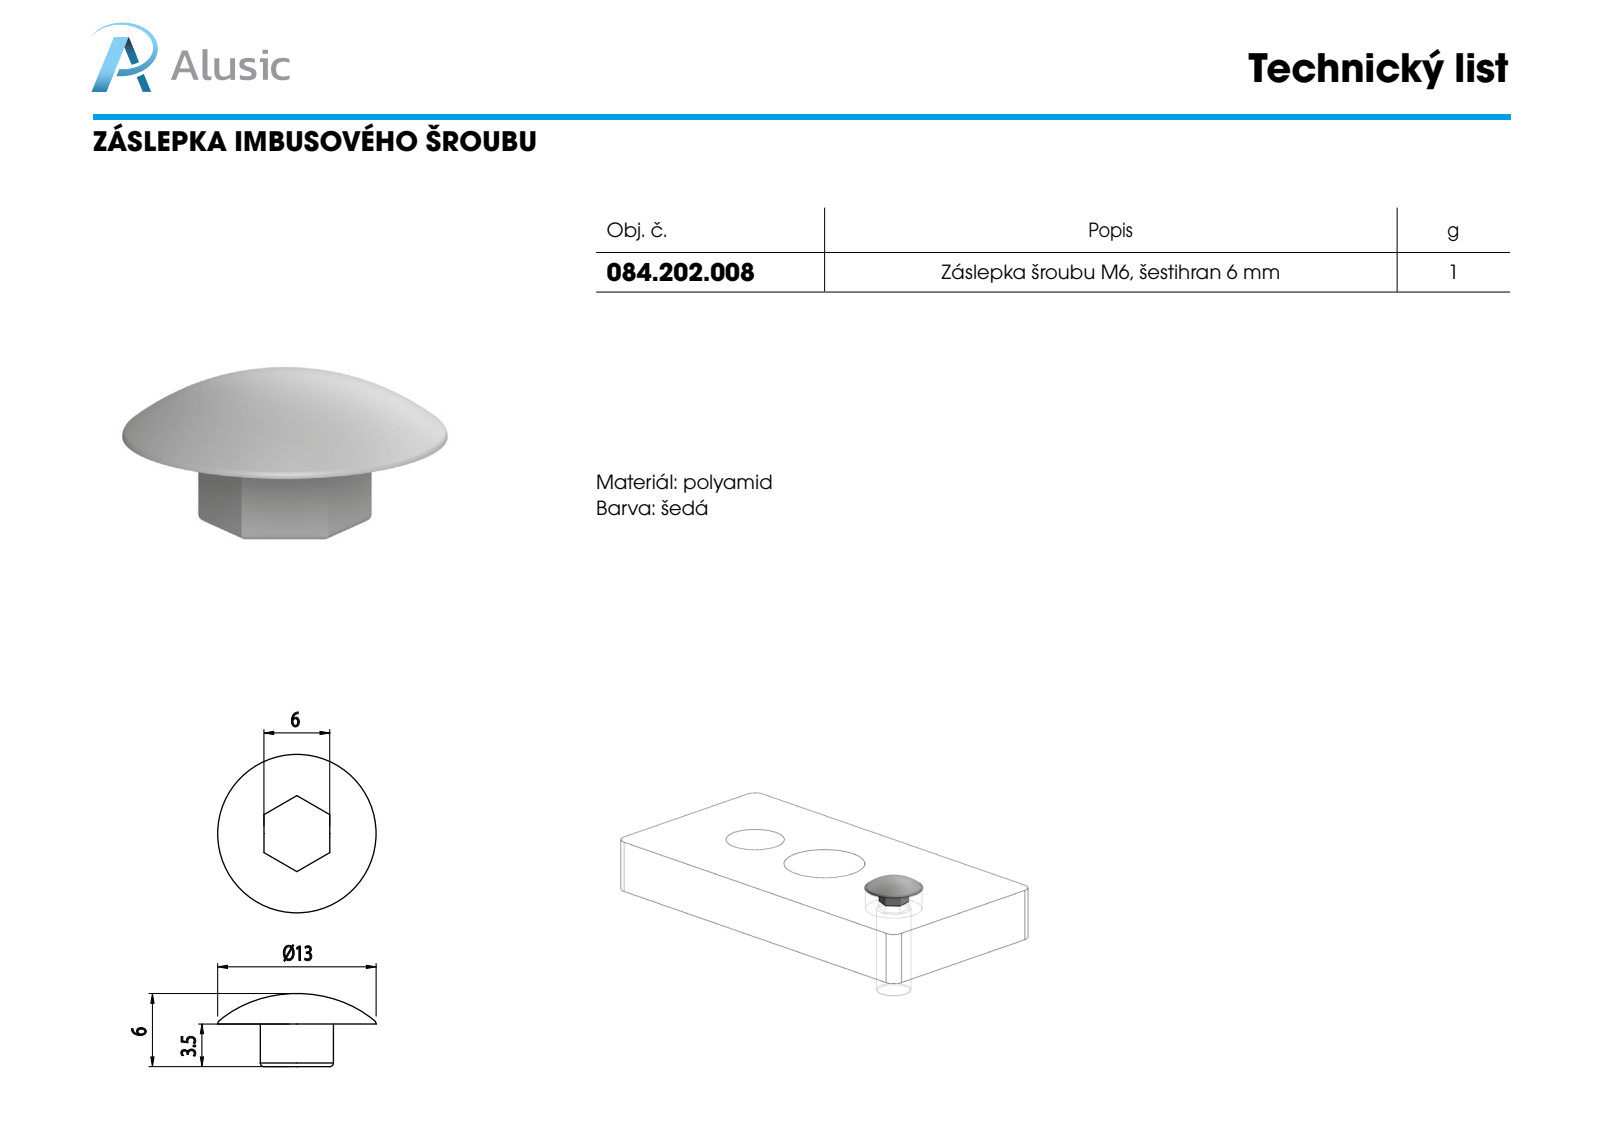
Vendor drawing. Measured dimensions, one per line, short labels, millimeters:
name: 084.202.008
written by: SolidWorks 2011 (CONFIG_CONTROL_DESIGN)
unit: mm
bodies: 1 solid, 37 faces (15 planar, 18 cylindrical, 4 other)
size: 13 × 13 × 6
volume: 244 mm³; area: 403 mm²
rounds: 18× R0.3
face distances: 1, 5, 6, 4, 3.5
